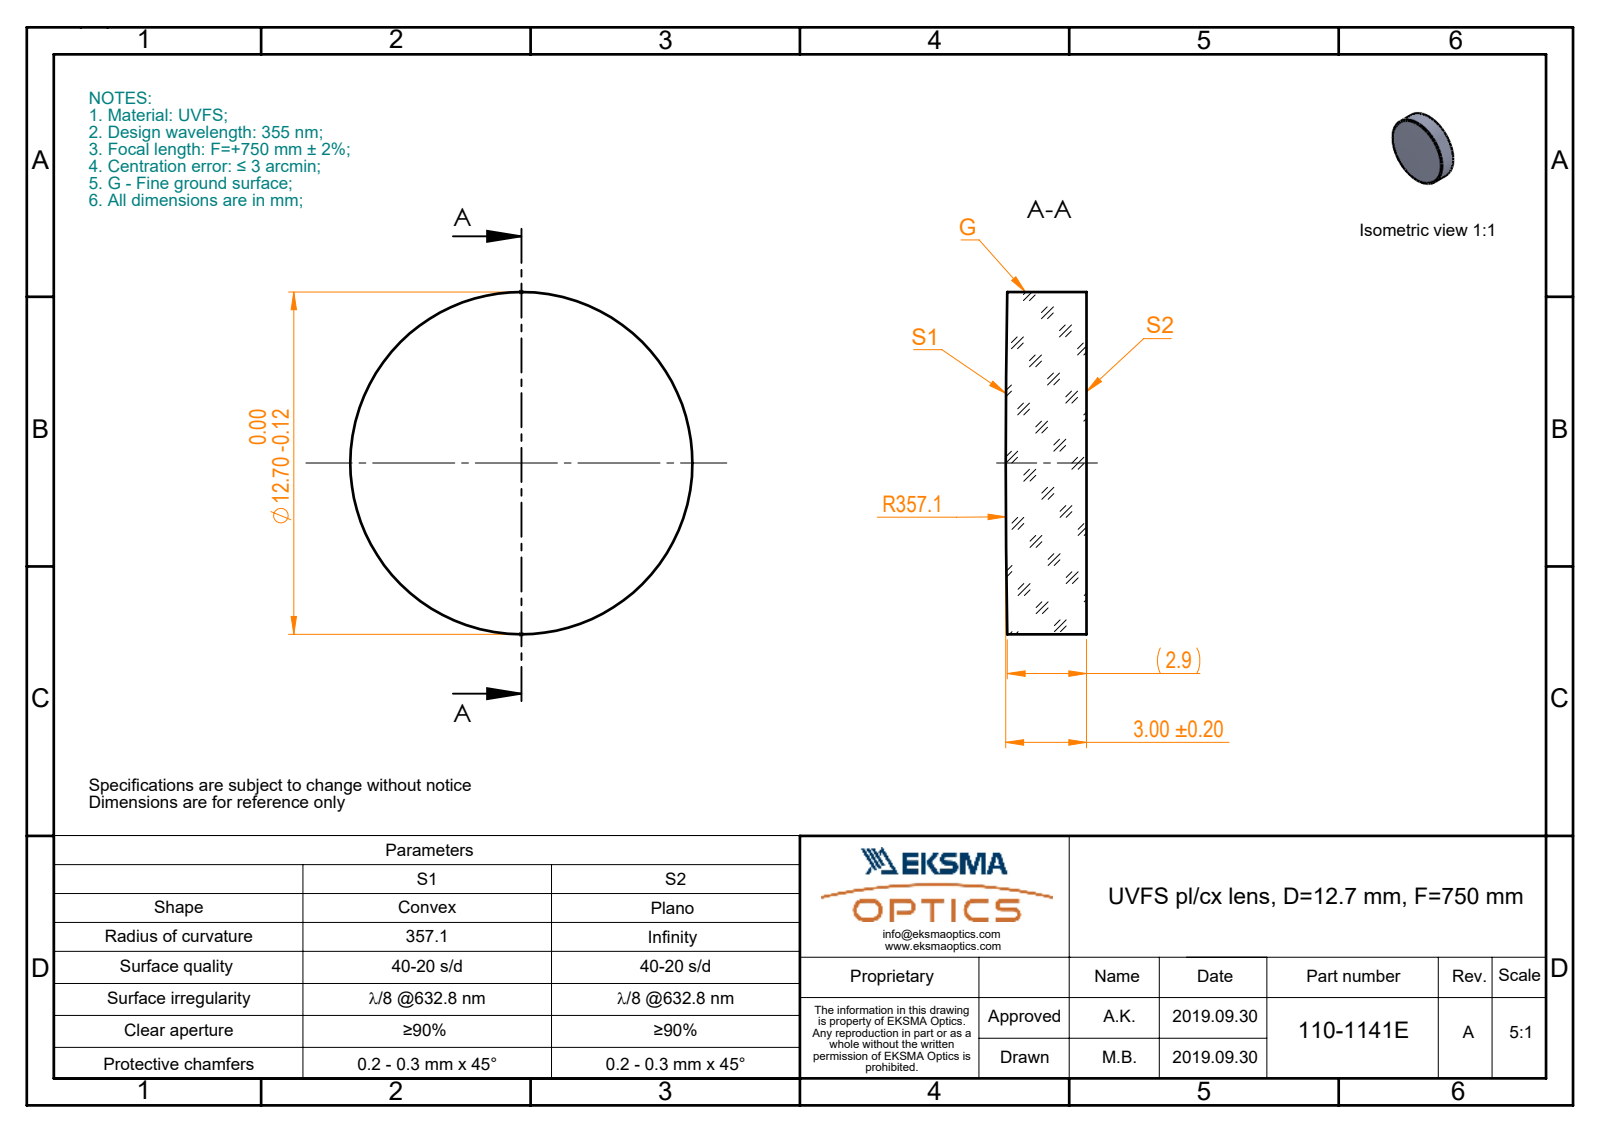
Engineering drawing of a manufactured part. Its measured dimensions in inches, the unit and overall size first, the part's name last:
Units: inches
Overall size (bounding box): 0.5 × 0.5 × 0.118
Round bosses / shafts (diameter × count): ⌀0.5 ×1
Volume: 0.023 in³ · Surface area: 0.575 in²
Bodies: 1 solid, 4 faces (1 planar, 2 cylindrical, 1 other)
Part name (STEP PRODUCT): 110-1141E UVFS pl-cx 12.7 F750
STEP written by: SolidWorks 2019 (CONFIG_CONTROL_DESIGN)
